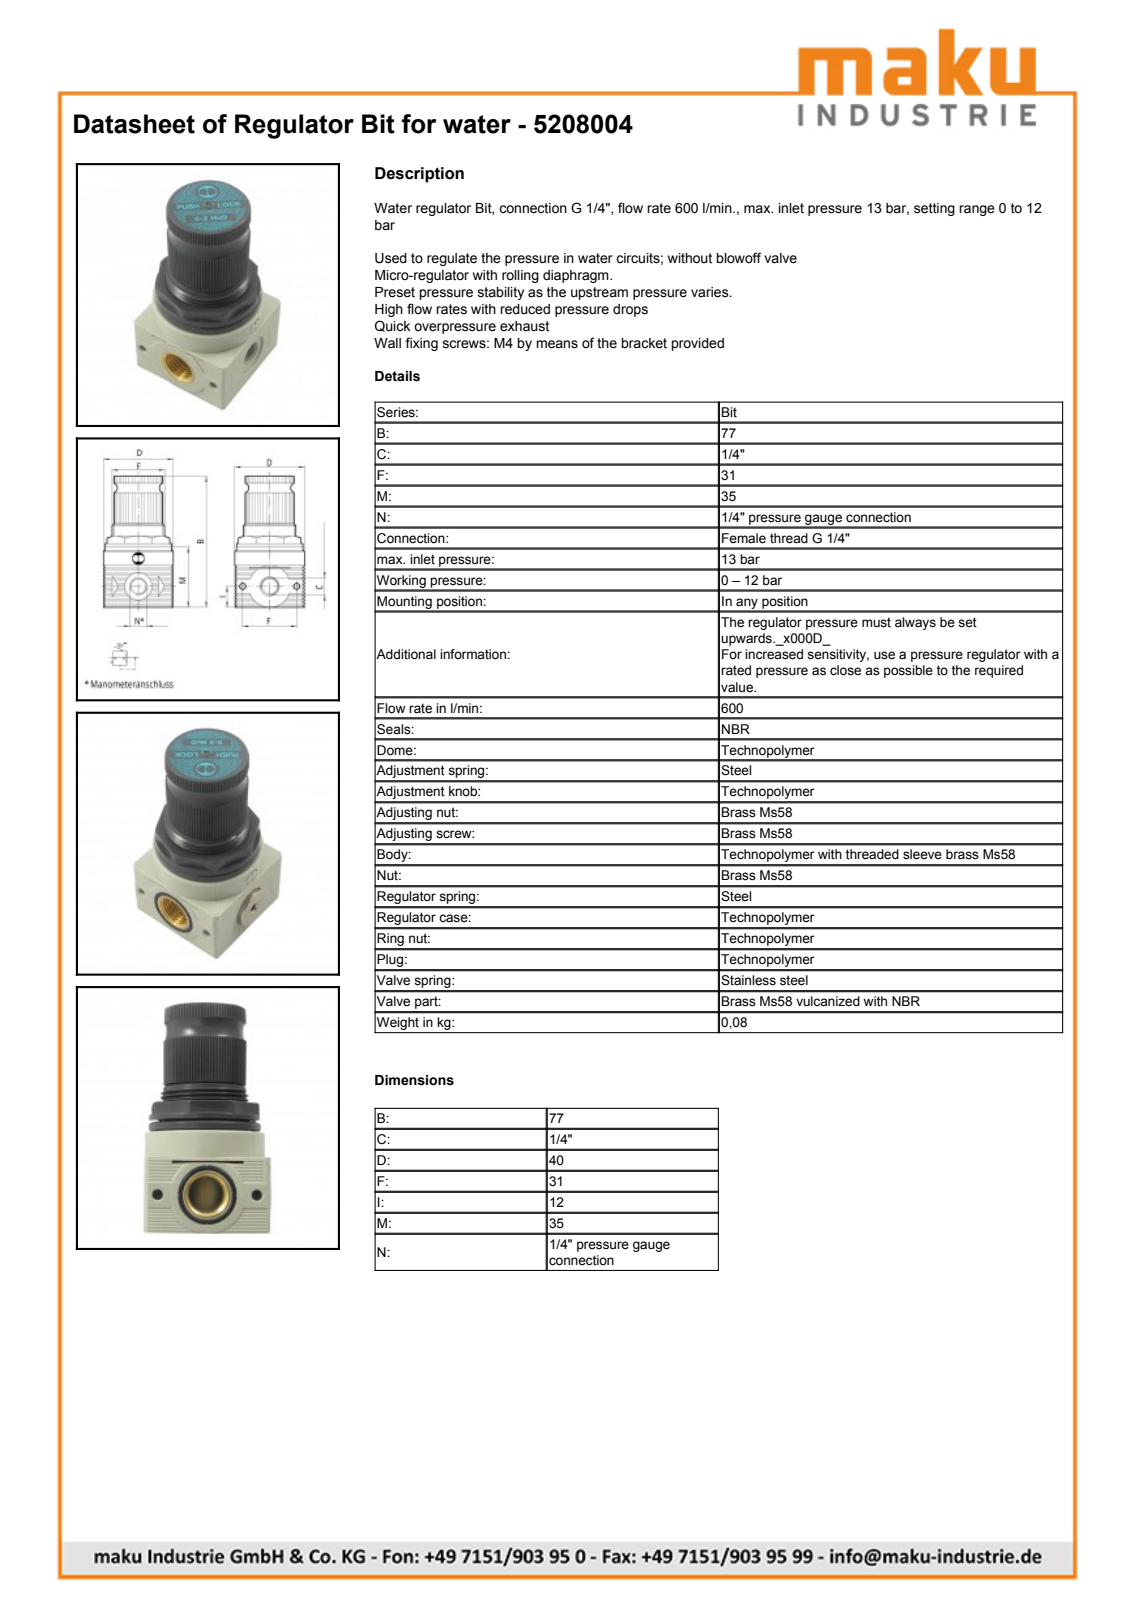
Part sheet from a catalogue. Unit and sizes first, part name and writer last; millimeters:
Units: millimetres
Overall size (bounding box): 77 × 41.5 × 40
Round holes (diameter × count): ⌀4 ×2, ⌀8.57 ×1, ⌀11.45 ×1, ⌀15.5 ×1
Round bosses / shafts (diameter × count): ⌀39.9 ×1, ⌀38 ×1, ⌀37.6 ×1, ⌀30 ×1, ⌀28 ×1, ⌀24 ×1, ⌀15 ×1, ⌀9.73 ×1
Partial cylindrical surfaces — rounded edges, fillets, slot ends (radius × count): R12 ×1
Main face-to-face distances: 32, 40, 1, 9, 10, 39.95, 77, 45, 39, 19
Hole centre spacings: 15.5, 31
Volume: 76 444 mm³ · Surface area: 18 319 mm²
Bodies: 3 solids, 127 faces (92 planar, 27 cylindrical, 8 other)
Part name (STEP PRODUCT): 5208004; 5208004-BD; 5208004-KN; 1/8-BIT
STEP written by: PARTsolutions (AUTOMOTIVE_DESIGN)
